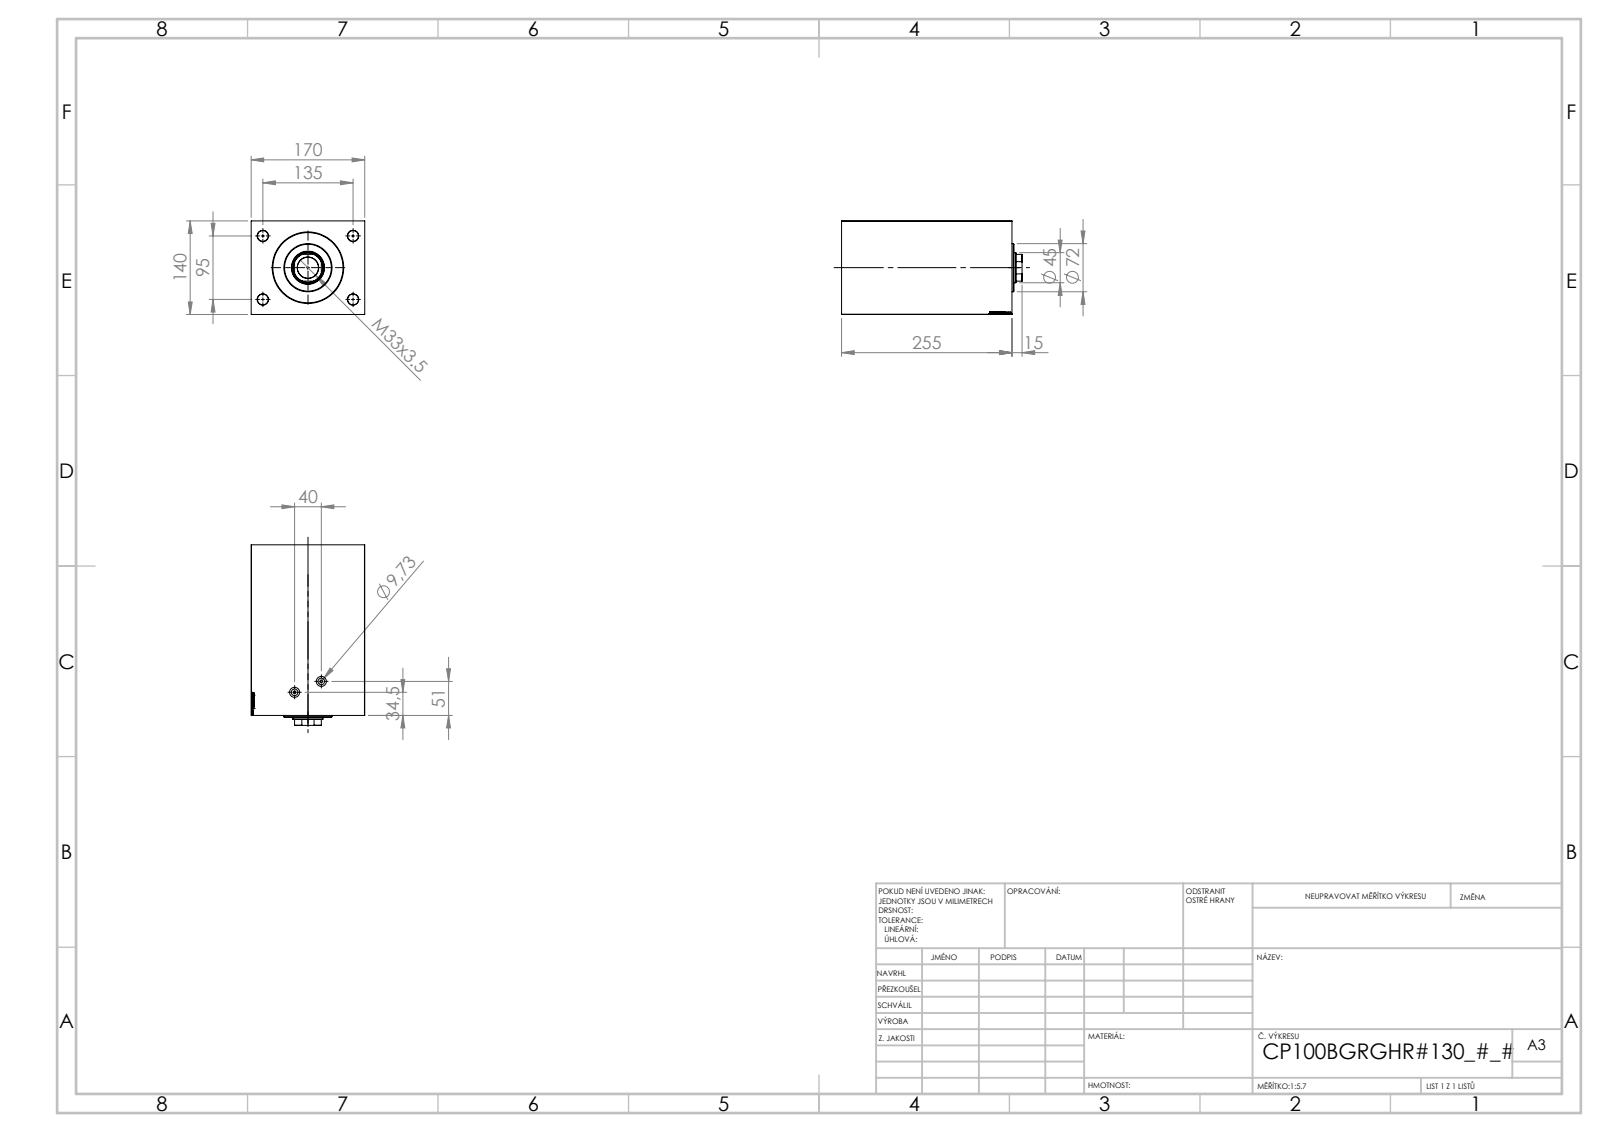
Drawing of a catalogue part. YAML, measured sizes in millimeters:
part_name: "V450CP_B_VCP; V450CP_B; V450CP_VC_B"
step_written_by: "SolidWorks 2019 (CONFIG_CONTROL_DESIGN)"
units: millimeters
bodies: {solids: 3, faces: 899, planar: 405, cylindrical: 64, other: 430}
overall_size: [270, 170, 140]
volume: 5180000
surface_area: 404536
round_holes:
  - {diameter: 16, count: 4}
  - {diameter: 4, count: 2}
  - {diameter: 8.5, count: 2}
  - {diameter: 9.73, count: 2}
  - {diameter: 15, count: 2}
  - {diameter: 16.66, count: 2}
  - {diameter: 31.5, count: 1}
  - {diameter: 45, count: 1}
  - {diameter: 48.5, count: 1}
  - {diameter: 49.5, count: 1}
  - {diameter: 100, count: 1}
  - {diameter: 102, count: 1}
round_bosses_or_shafts:
  - {diameter: 72, count: 1}
partial_cylinders:
  - {radius: 22, count: 1}
face_to_face_distances: [140, 170, 255, 26, 229, 186, 160, 69, 56, 30]
hole_center_spacings: [82.54, 47.71, 59.9, 95, 109.35, 135, 147.37, 165.08]
